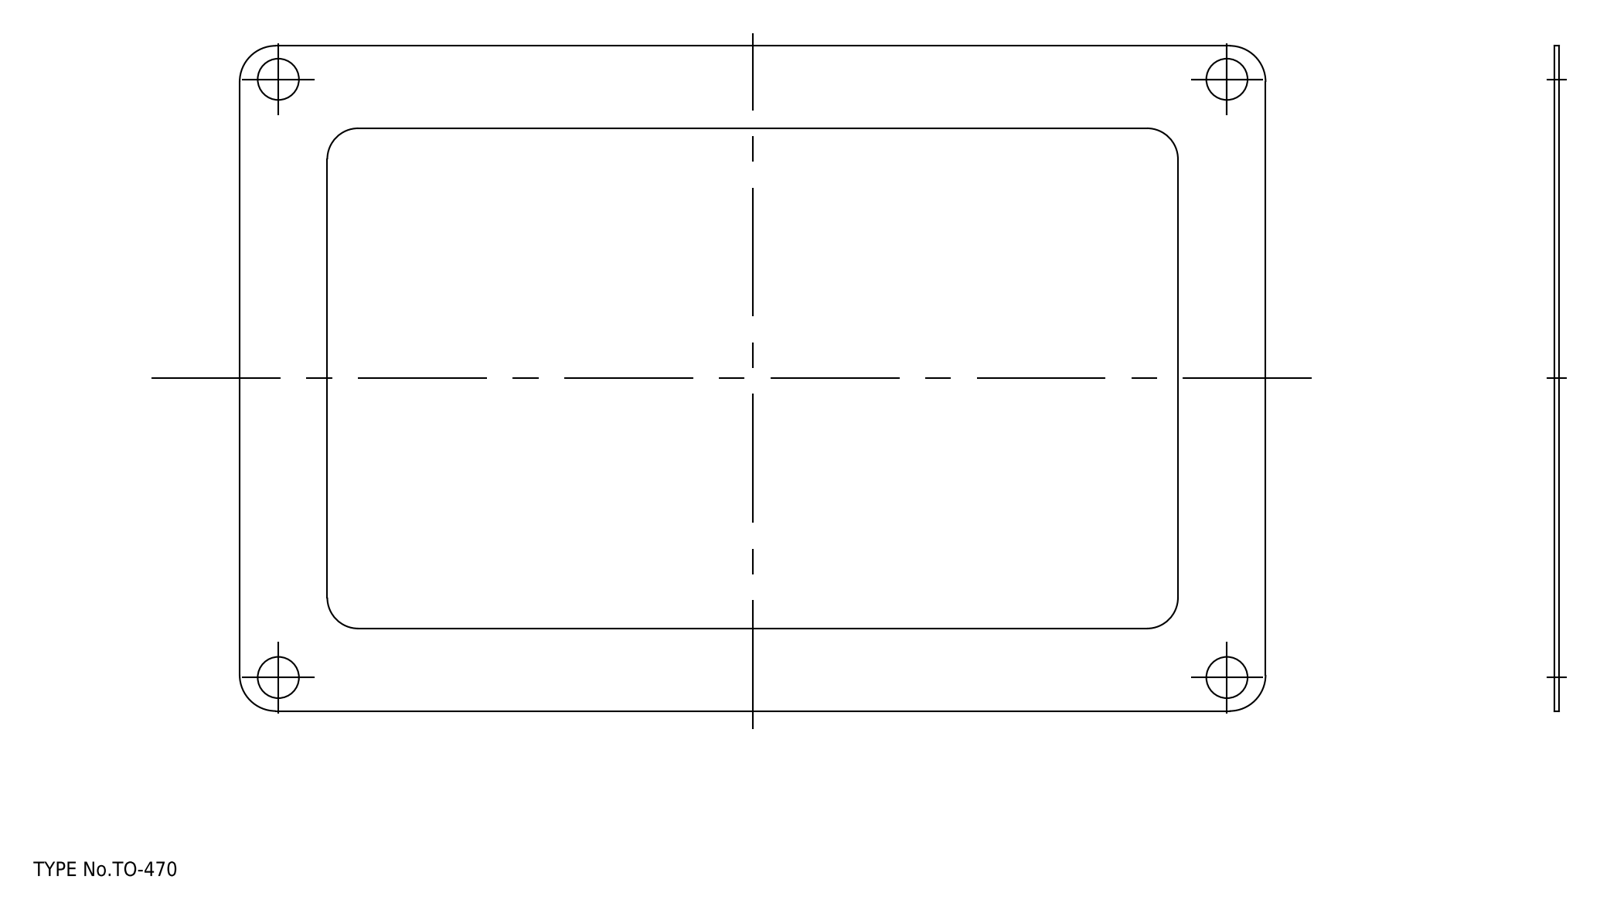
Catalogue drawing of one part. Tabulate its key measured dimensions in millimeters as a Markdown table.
| quantity | value |
| --- | --- |
| STEP written by | spGate 16.7.1 (AUTOMOTIVE_DESIGN) |
| units | millimeters |
| bodies | 1 solid, 26 faces (10 planar, 16 cylindrical, 0 other) |
| overall size | 199 × 129 × 1 |
| volume | 9 454 mm³ |
| surface area | 20 166 mm² |
| round holes (diameter × count) | 8 × 4 |
| partial cylindrical surfaces (radius × count) | 6 × 4, 7 × 4 |
| main face-to-face distances | 1, 16, 113, 129, 17, 182, 97, 199, 165 |
| hole center spacings | 116, 184, 217.51 |
